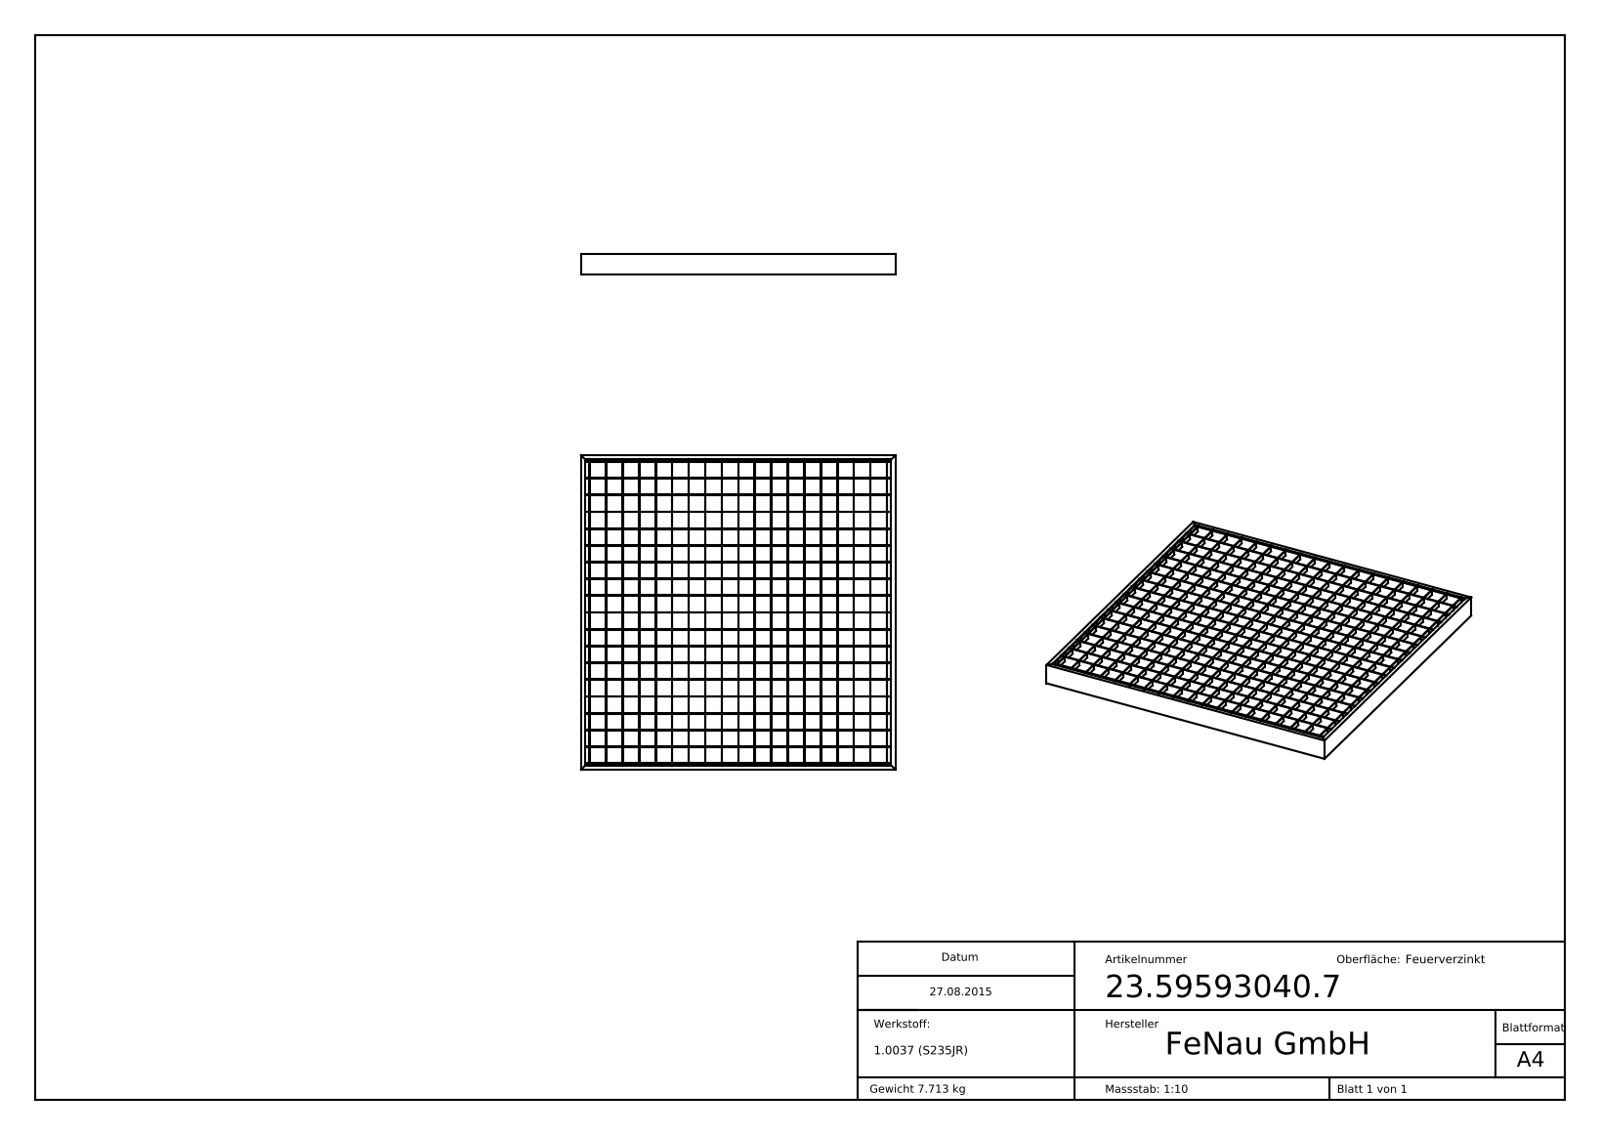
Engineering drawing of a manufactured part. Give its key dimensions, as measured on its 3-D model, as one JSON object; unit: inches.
{"part_name": "23-59593040-7", "step_written_by": "SolidWorks 2015 (CONFIG_CONTROL_DESIGN)", "units": "inches", "bodies": {"solids": 1, "faces": 1388, "planar": 1388, "cylindrical": 0, "other": 0}, "overall_size": [23.228, 23.228, 1.575], "volume_in3": 60.34, "surface_area_in2": 2124, "face_to_face_distances": [1.24, 2.48, 3.72, 4.961, 6.201, 7.441, 8.681, 9.921, 11.161, 12.402]}
